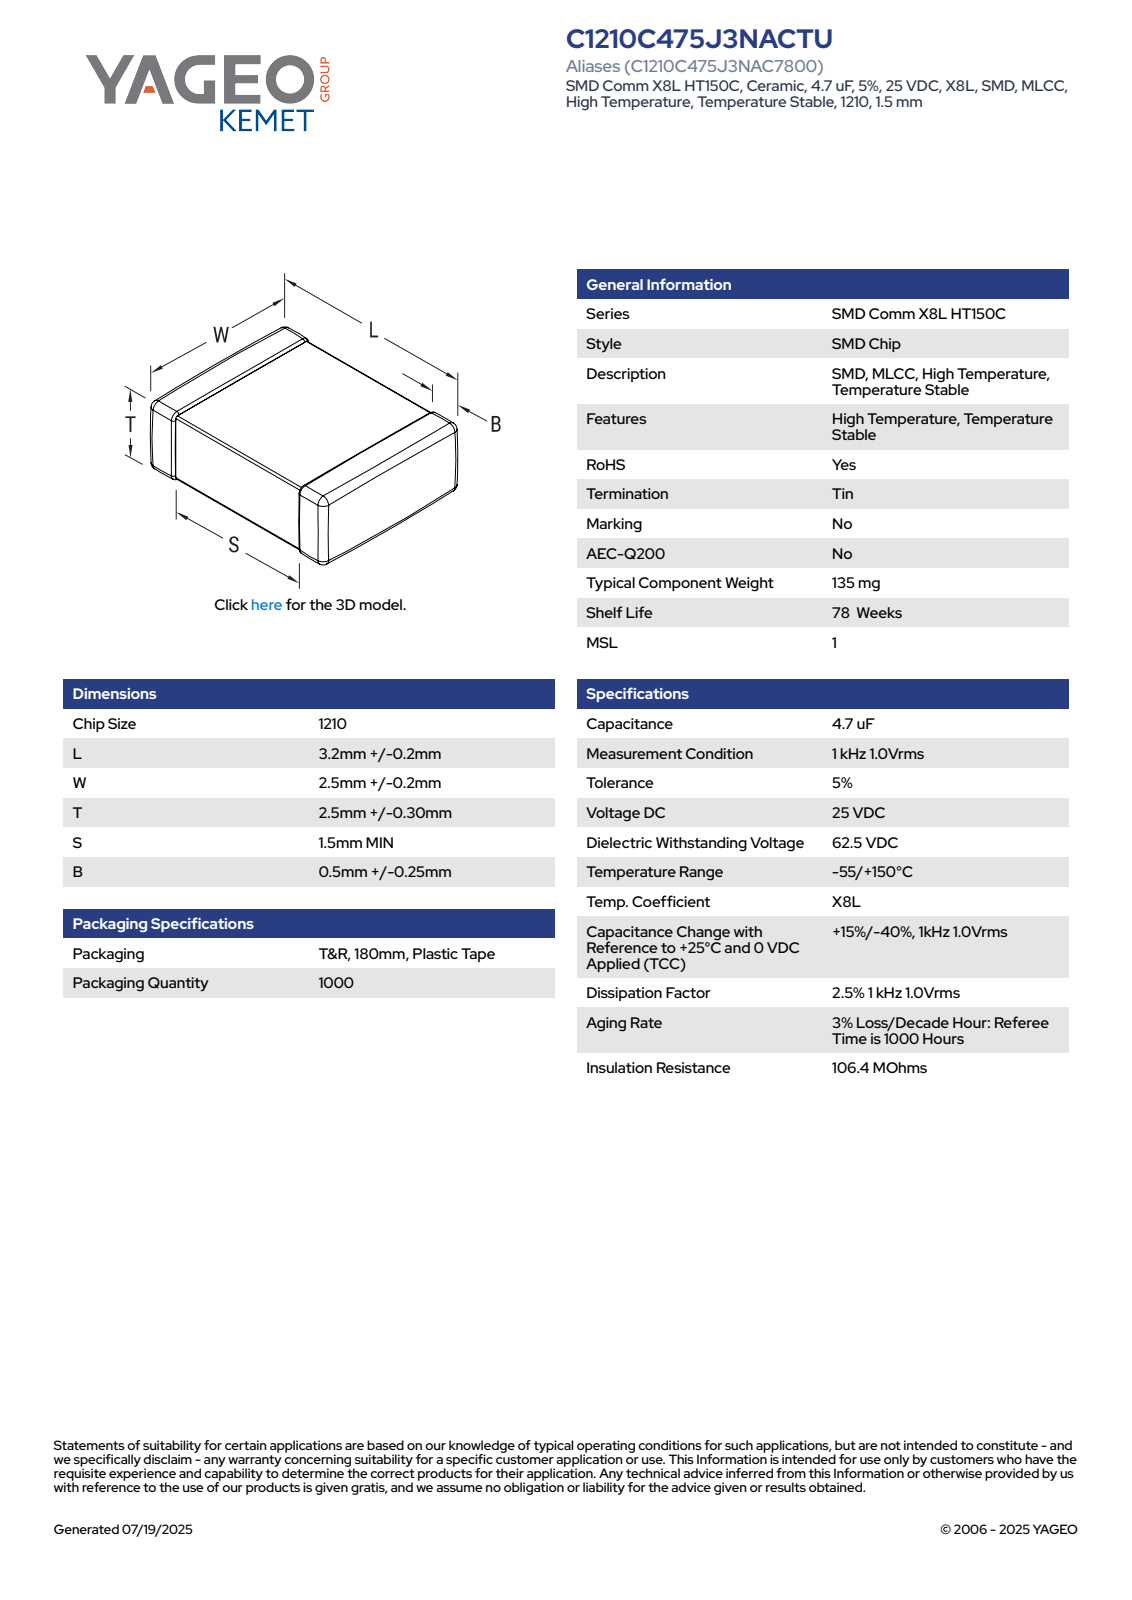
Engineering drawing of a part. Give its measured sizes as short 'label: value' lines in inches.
name: CCS_CCSTD_1210_L3.4W2.7S2.5T2.8B0.5
written by: SolidWorks 2021 (AUTOMOTIVE_DESIGN)
unit: in
bodies: 4 solids, 125 faces (71 planar, 38 cylindrical, 16 other)
size: 0.134 × 0.11 × 0.106
volume: 0.002 in³; area: 0.081 in²
face distances: 0.134, 0.104, 0.108, 0.102, 0.106, 0.106, 0.11, 0.108, 0.106, 0.016
